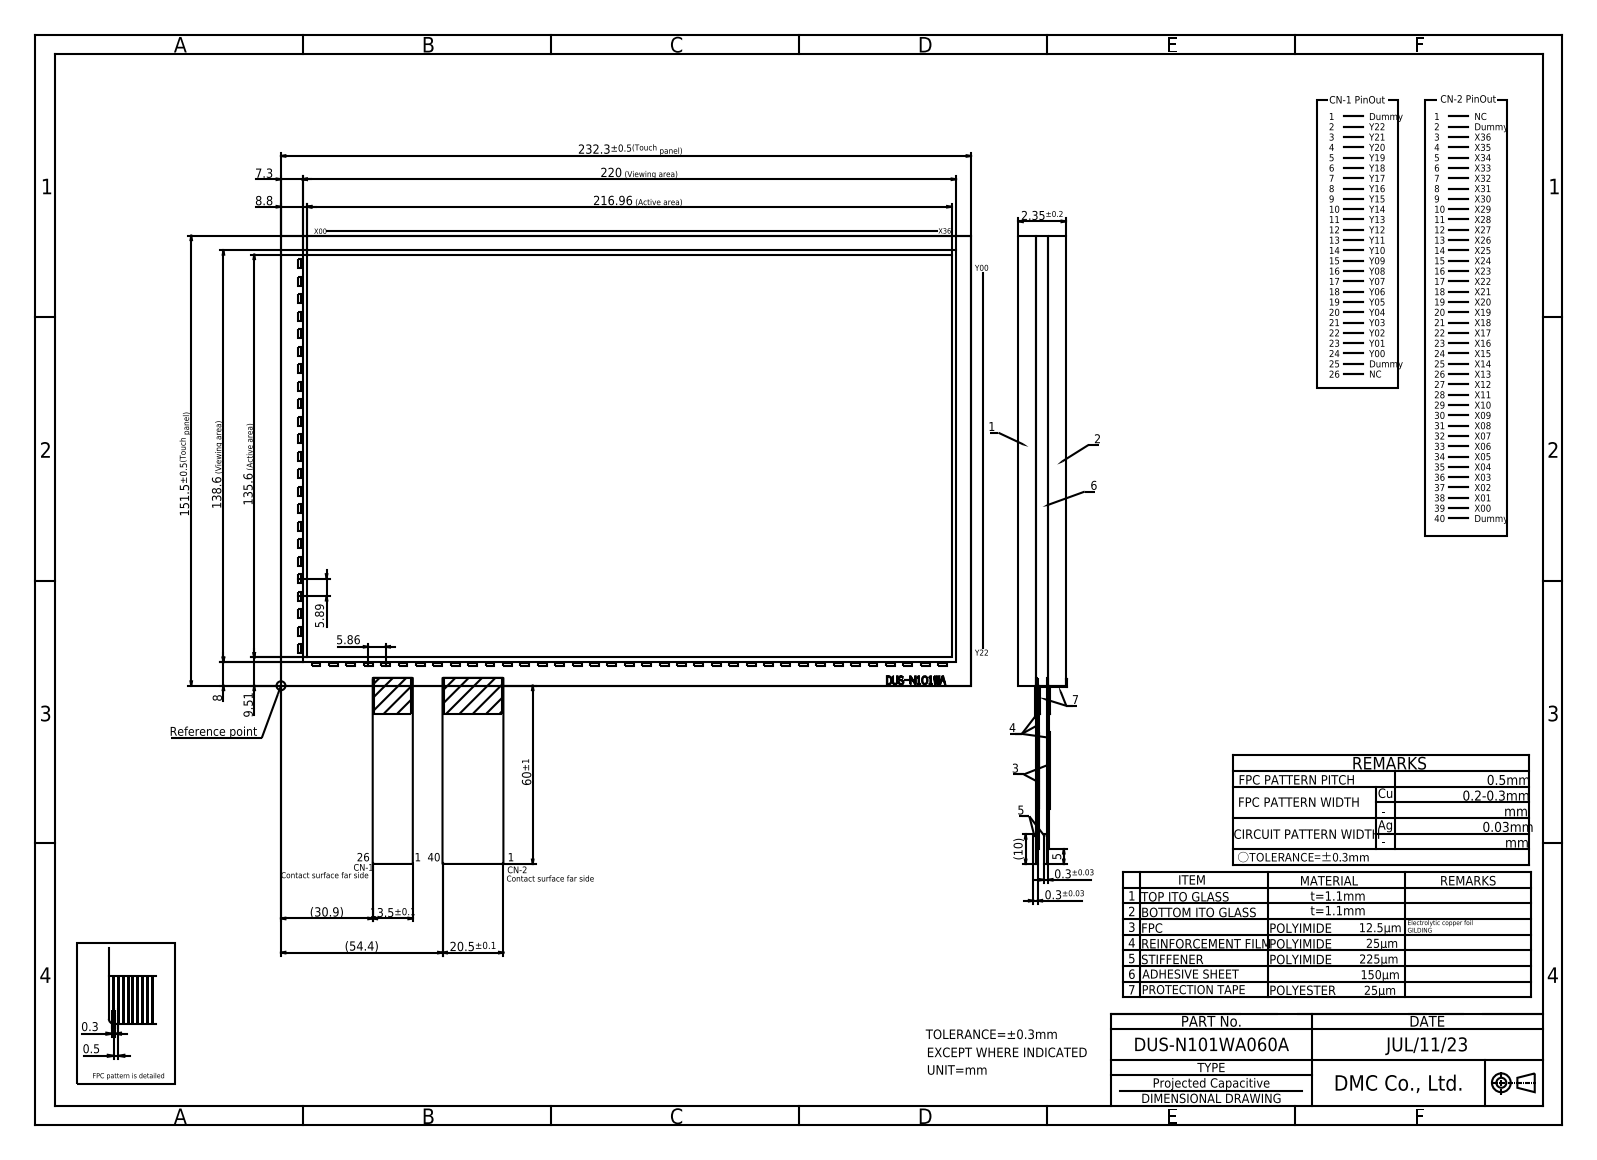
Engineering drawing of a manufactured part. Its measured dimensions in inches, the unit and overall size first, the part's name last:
Units: inches
Overall size (bounding box): 12.804 × 9.52 × 0.093
Partial cylindrical surfaces — rounded edges, fillets, slot ends (radius × count): R0.008 ×4
Main face-to-face distances: 0.093, 0.044, 0.048, 0.049, 0.043, 0.039, 0.089, 0.044, 5.965, 9.146
Volume: 5.061 in³ · Surface area: 118.5 in²
Bodies: 1 solid, 302 faces (298 planar, 4 cylindrical, 0 other)
Part name (STEP PRODUCT): DUS-N101WA060A
STEP written by: Autodesk Inventor 2020 (CONFIG_CONTROL_DESIGN)
